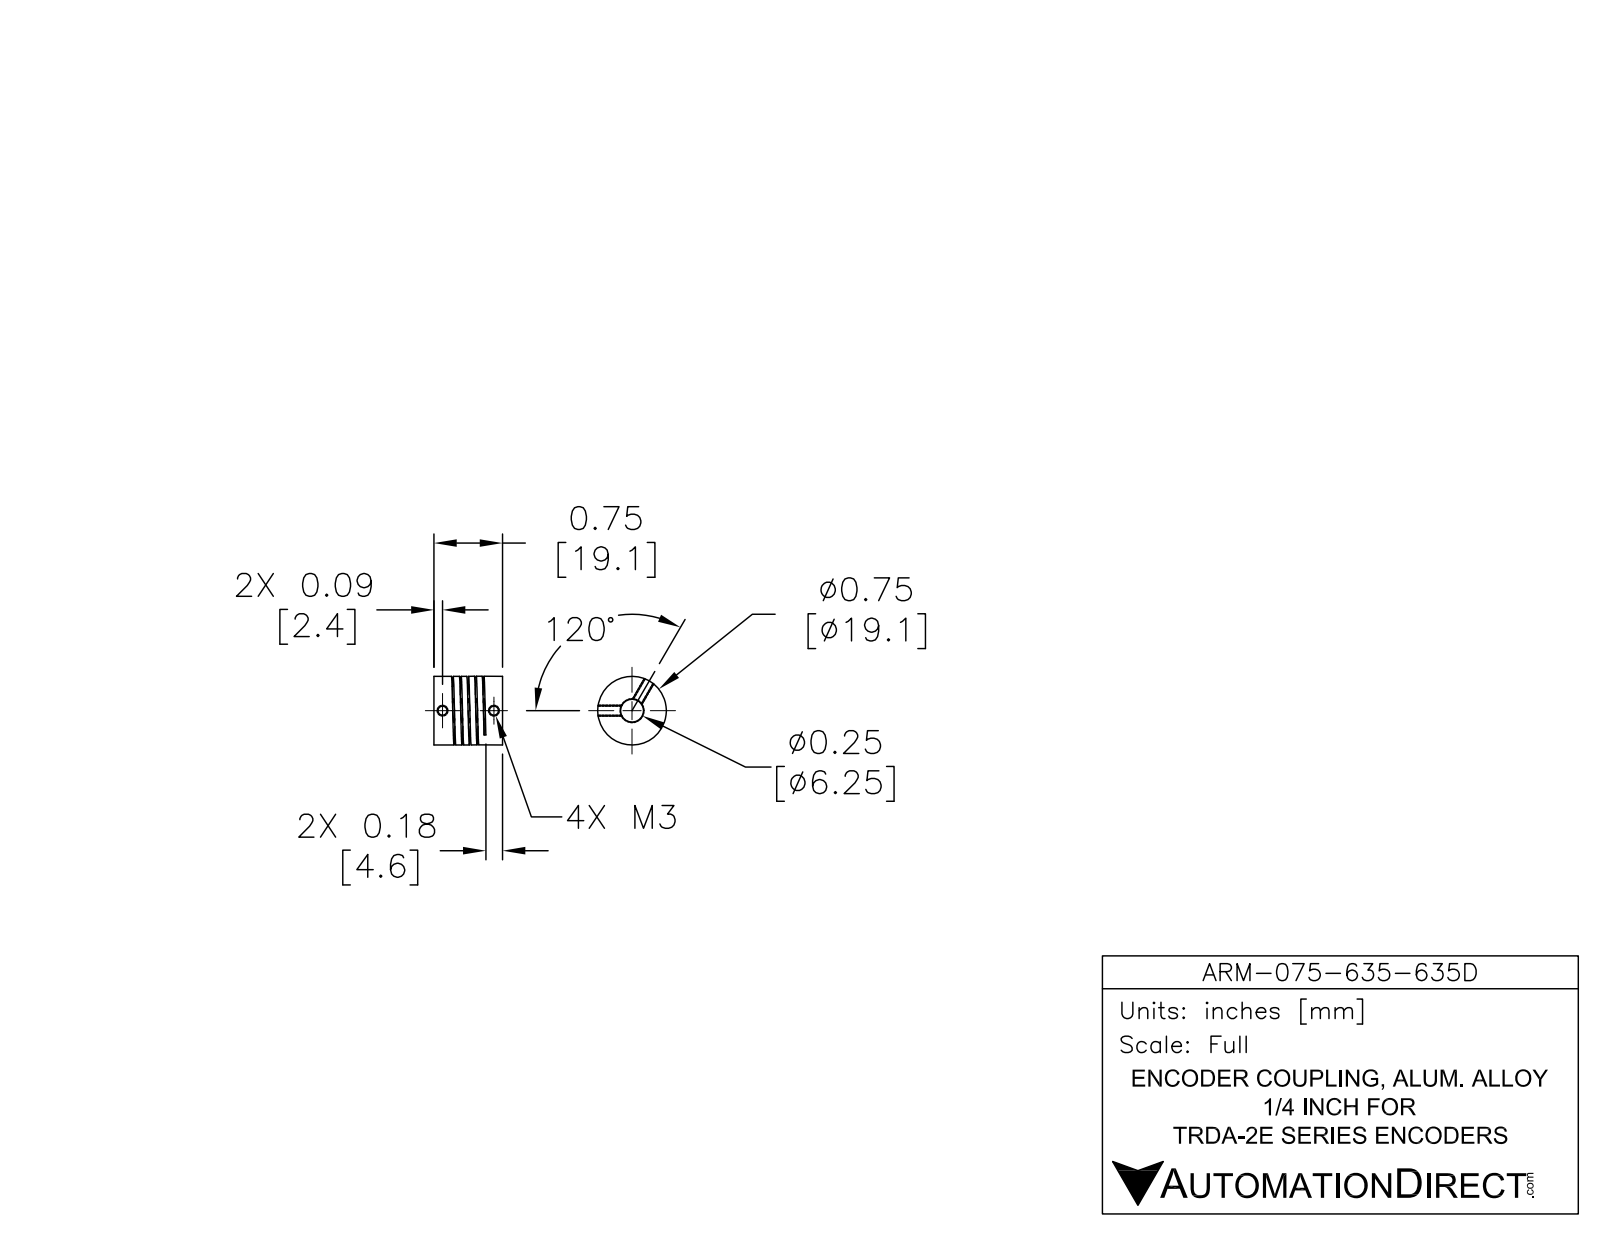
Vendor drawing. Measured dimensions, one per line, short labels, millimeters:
name: ARM-075-635-635D
written by: SolidWorks 2016 (AUTOMOTIVE_DESIGN)
unit: mm
bodies: 1 solid, 138 faces (58 planar, 40 cylindrical, 40 other)
size: 19.1 × 19.1 × 19.1
volume: 4 045 mm³; area: 4 141 mm²
holes: 4× ⌀3, 1× ⌀6.35, 1× ⌀8
bosses: 1× ⌀19.1
face distances: 19.1, 4.6, 14.5, 9.9, 1.5, 12.38, 13.88, 10.88, 0.75, 6.17
hole spacings: 14.3
